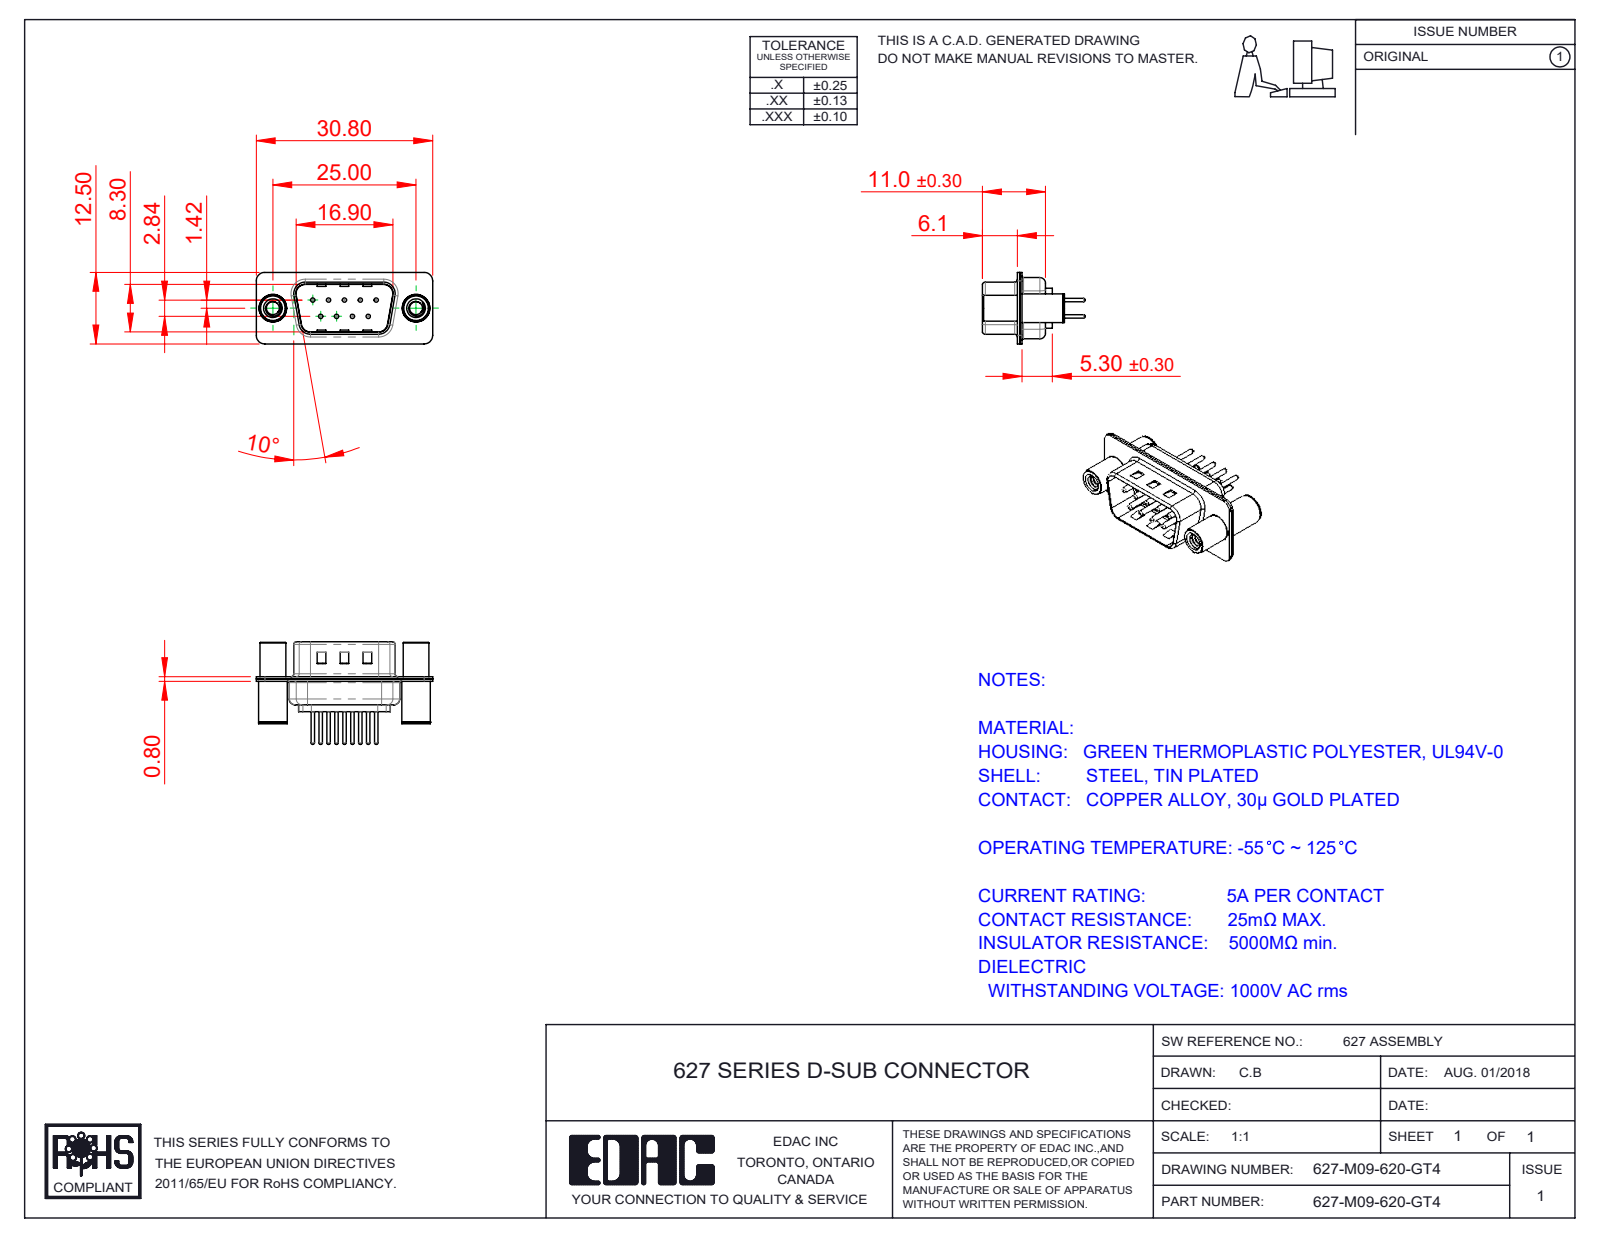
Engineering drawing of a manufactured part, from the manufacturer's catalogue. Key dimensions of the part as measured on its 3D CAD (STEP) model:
Part name (STEP PRODUCT): 627M 4-40 Threaded Standoff and Board Spacer; 627M Contact Row 1_20; 627M Contact Row 2_20; 627M Shell Front_09 Contacts (+3 more)
STEP written by: SolidWorks 2020 (CONFIG_CONTROL_DESIGN)
Units: millimetres
Bodies: 14 solids, 723 faces (176 planar, 307 cylindrical, 240 other)
Overall size (bounding box): 30.8 × 17.9 × 12.5
Volume: 1 597 mm³ · Surface area: 4 103 mm²
Round holes (diameter × count): ⌀0.75 ×9, ⌀1.6 ×9, ⌀2 ×9, ⌀2.26 ×2, ⌀3.26 ×2, ⌀4 ×2, ⌀4.8 ×2
Round bosses / shafts (diameter × count): ⌀1.5 ×9, ⌀0.6 ×9, ⌀5 ×2, ⌀4.9 ×2, ⌀4.5 ×2
Partial cylindrical surfaces — rounded edges, fillets, slot ends (radius × count): R1.5 ×16, R2 ×12, R0.5 ×8, R1.6 ×8, R0.25 ×4, R0.6 ×4, R0.65 ×4, R0.9 ×4
Main face-to-face distances: 0.4, 0.8, 9.5, 9.1, 8.7, 0.65, 9.9, 1.2, 5.3, 6.1
Hole centre spacings: 3.16, 2.77, 5.54, 5.03, 5.04, 8.31, 7.1, 7.48
